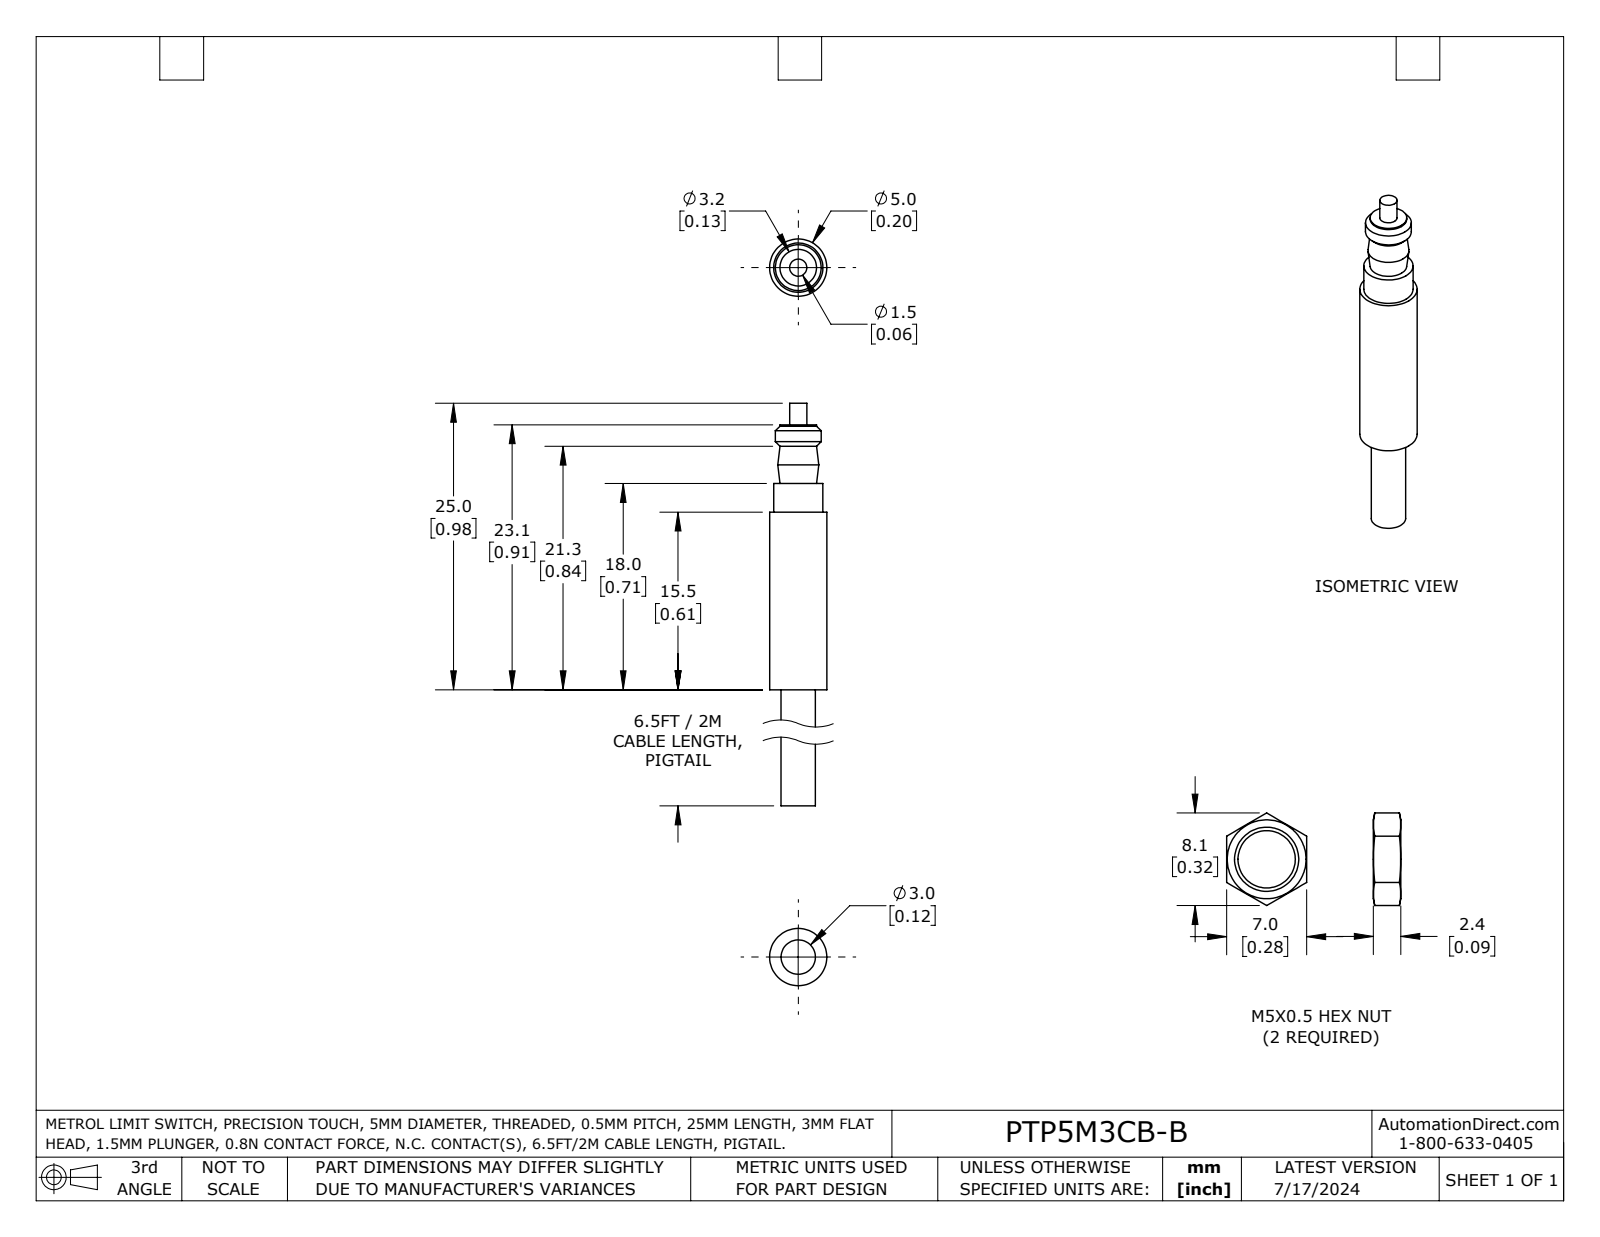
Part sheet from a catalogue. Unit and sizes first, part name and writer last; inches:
Units: inches
Overall size (bounding box): 1.339 × 0.197 × 0.197
Round bosses / shafts (diameter × count): ⌀0.197 ×1, ⌀0.169 ×1, ⌀0.157 ×1, ⌀0.138 ×1, ⌀0.126 ×1, ⌀0.059 ×1
Main face-to-face distances: 0.354, 1.063, 0.709, 1.265, 0.911, 0.202, 0.965, 0.61, 0.098, 0.3
Volume: 0.029 in³ · Surface area: 0.752 in²
Bodies: 1 solid, 16 faces (6 planar, 6 cylindrical, 4 other)
Part name (STEP PRODUCT): PTP5M3CB-B
STEP written by: SolidWorks 2023 (AUTOMOTIVE_DESIGN)
